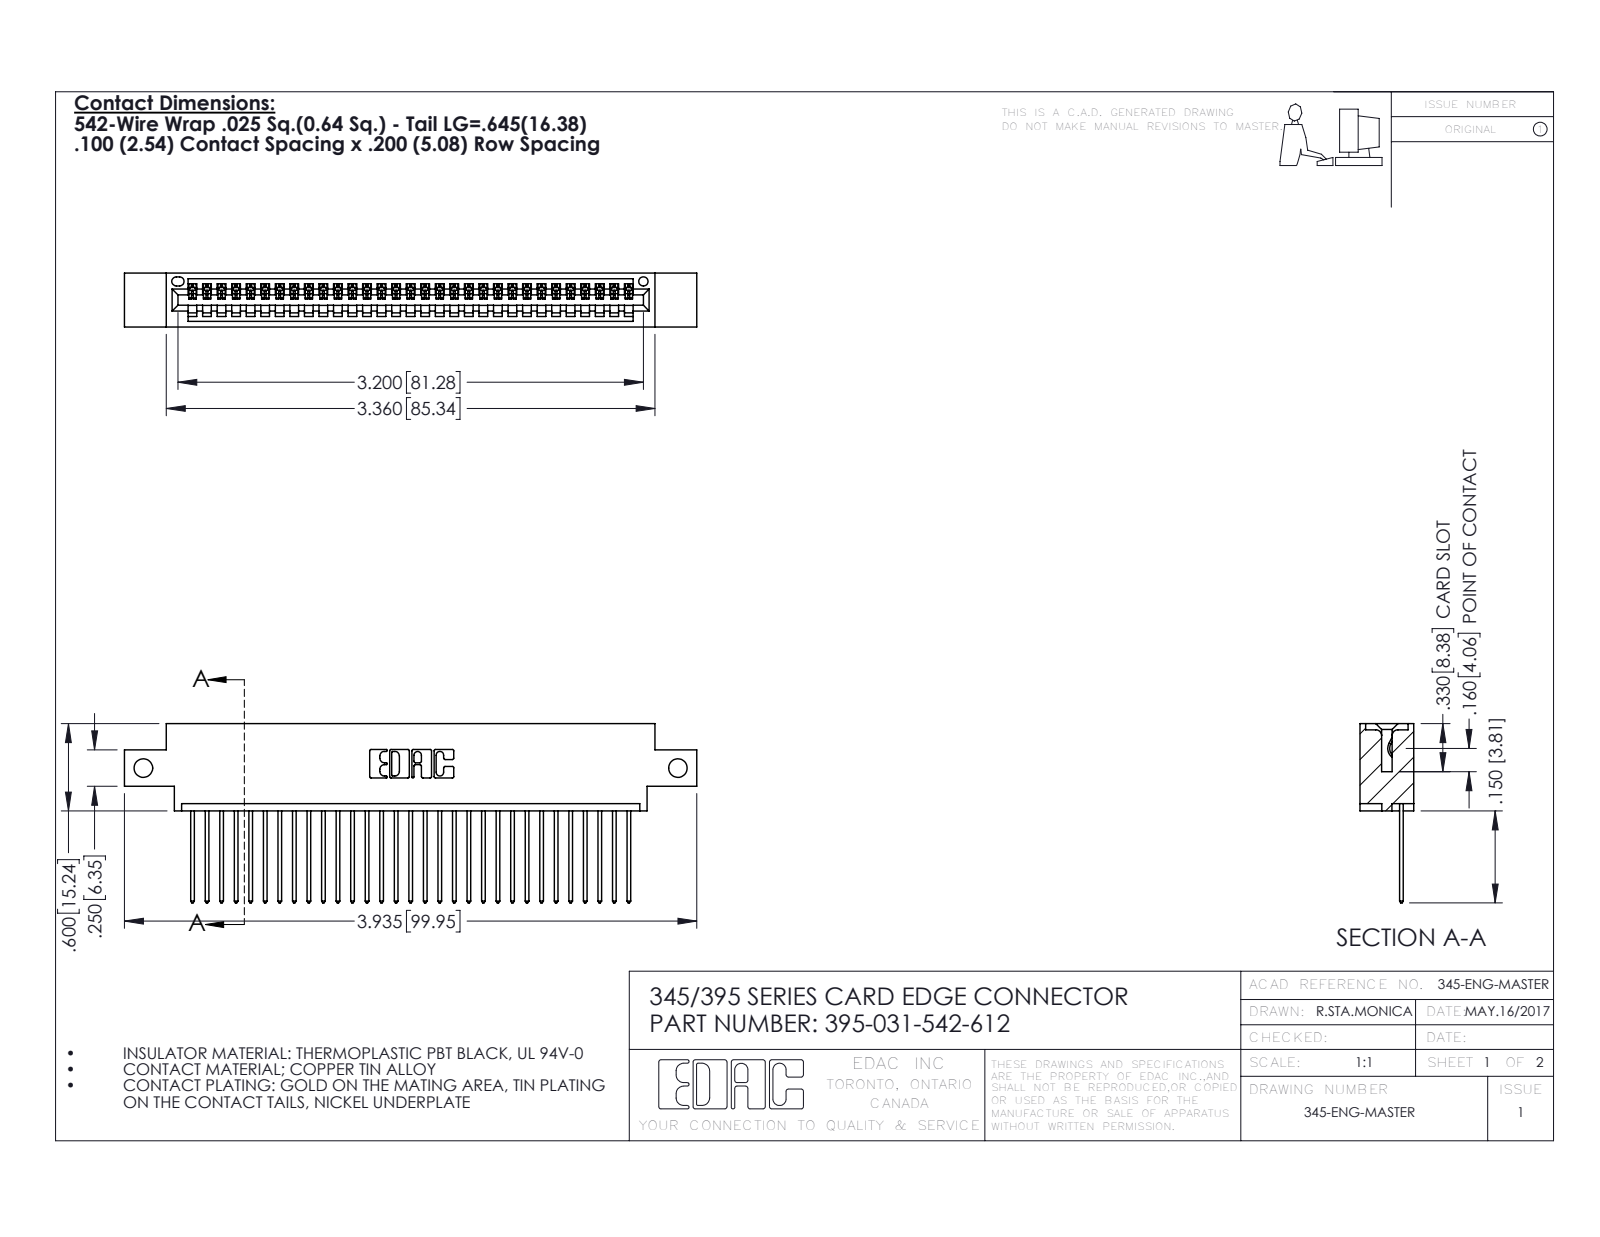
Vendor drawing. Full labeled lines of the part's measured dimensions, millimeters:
Part name (STEP PRODUCT): 345 Part_0.170 Offset - Side Mount; 345-292-001_345-293-142; 395-031-542-612
STEP written by: SolidWorks 2016 (CONFIG_CONTROL_DESIGN)
Units: millimetres
Bodies: 32 solids, 1928 faces (1324 planar, 604 cylindrical, 0 other)
Overall size (bounding box): 99.9 × 31.3 × 9.4
Volume: 9 280 mm³ · Surface area: 12 590 mm²
Round holes (diameter × count): ⌀3.3 ×2, ⌀1.6 ×1
Partial cylindrical surfaces — rounded edges, fillets, slot ends (radius × count): R0.2 ×62, R0.3 ×62, R0.3 ×22, R0.2 ×6, R0.8 ×6, R0.7 ×3, R0.8 ×2, R1 ×2
Main face-to-face distances: 7.6, 1.8, 9.4, 2.5, 6.9, 0.6, 5.1, 5.7, 4.4, 3.8
Hole centre spacings: 93.3
